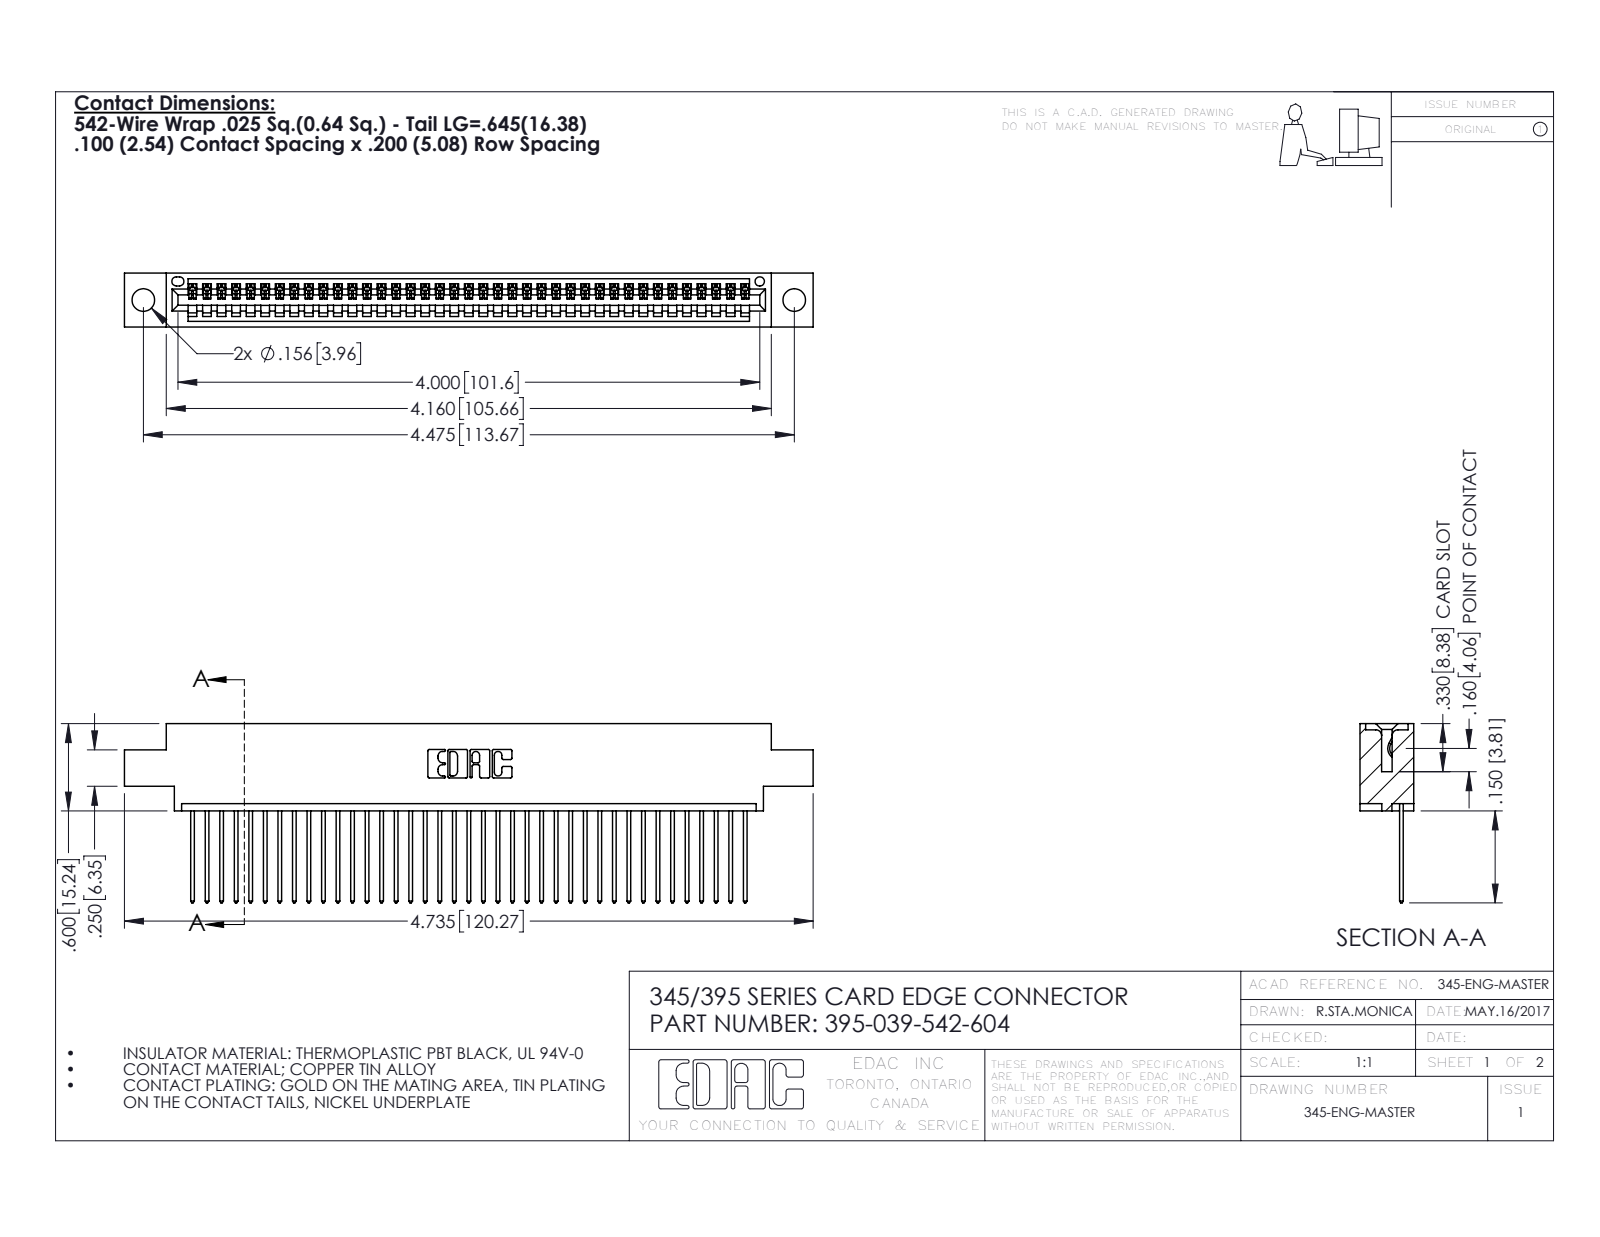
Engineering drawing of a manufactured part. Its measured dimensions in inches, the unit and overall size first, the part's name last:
Units: inches
Overall size (bounding box): 4.735 × 1.232 × 0.37
Round holes (diameter × count): ⌀0.156 ×2, ⌀0.064 ×1
Partial cylindrical surfaces — rounded edges, fillets, slot ends (radius × count): R0.006 ×78, R0.01 ×78, R0.01 ×22, R0.007 ×6, R0.031 ×6, R0.026 ×3, R0.031 ×2, R0.04 ×2
Main face-to-face distances: 0.072, 0.298, 0.37, 0.098, 0.272, 0.025, 0.2, 0.225, 0.175, 0.149
Hole centre spacings: 0.27, 4.239, 4.475
Volume: 0.689 in³ · Surface area: 23.93 in²
Bodies: 40 solids, 2392 faces (1644 planar, 748 cylindrical, 0 other)
Part name (STEP PRODUCT): 395-039-542-604; 345 Part_0.170 Offset - 0.156 Dia-TH; 345-292-001_345-293-142
STEP written by: SolidWorks 2016 (CONFIG_CONTROL_DESIGN)
